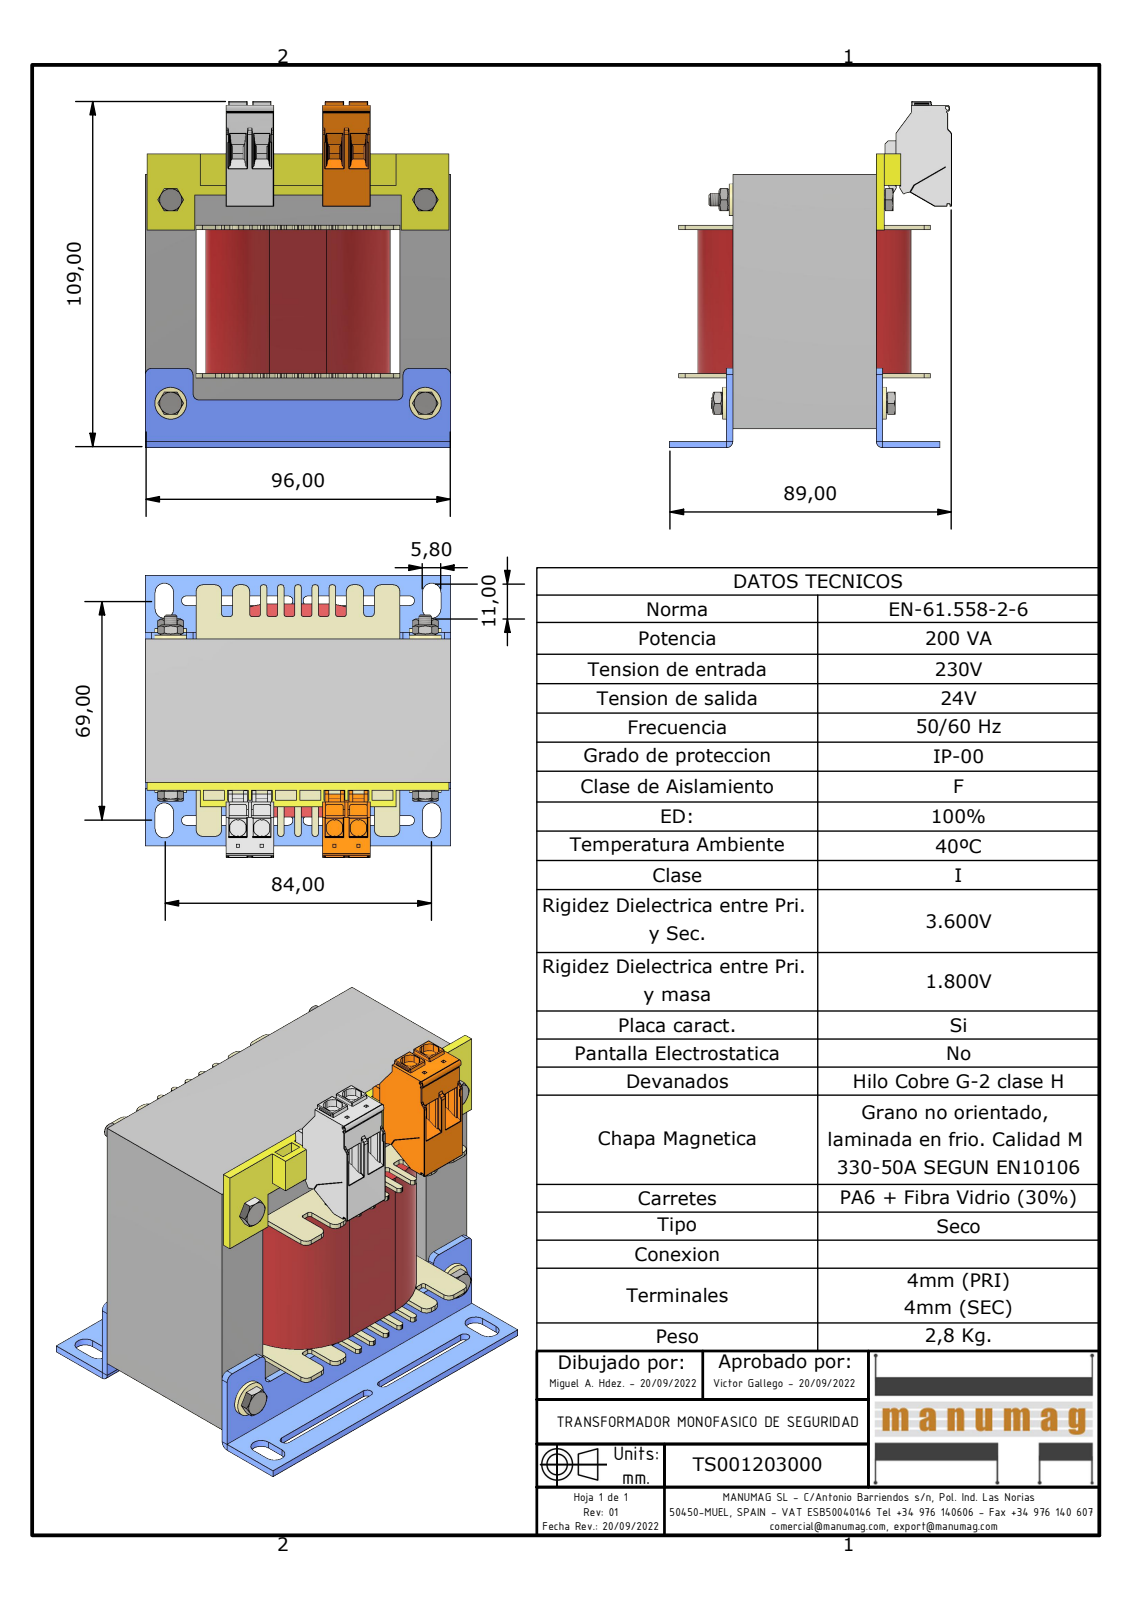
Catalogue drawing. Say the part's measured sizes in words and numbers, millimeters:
The part is named "TS001203000; EI96 x 80 - 45 (RC32); AF32DIN; centrador M4 (+6 more)". Its 3-D file was written by "Autodesk Inventor 2023 (AUTOMOTIVE_DESIGN)". It is 21 solids with 3890 faces: 3076 planar, 574 cylindrical and 240 other. Overall it measures 109 by 96 by 88.7 millimeters. Its volume is 406 861 cubic millimeters and its surface area 107 142 square millimeters. Round holes: 4 of diameter 3.24, 4 of diameter 4, 4 of diameter 5.5, 2 of diameter 5.8. Round bosses or shafts: 4 of diameter 10, 4 of diameter 5.9, 4 of diameter 4.9, 4 of diameter 3.62. Partial cylindrical surfaces (rounded edges, fillets, slot ends): 160 of radius 0.15, 51 of radius 0.8, 48 of radius 0.2, 22 of radius 2, 12 of radius 0.5, 8 of radius 1.5, 8 of radius 2.9, 7 of radius 0.3. The main face-to-face distances are 16, 64, 32, 45, 48, 80, 2, 96, 20, 47. The hole center spacings are 64, 80, 102.45.
